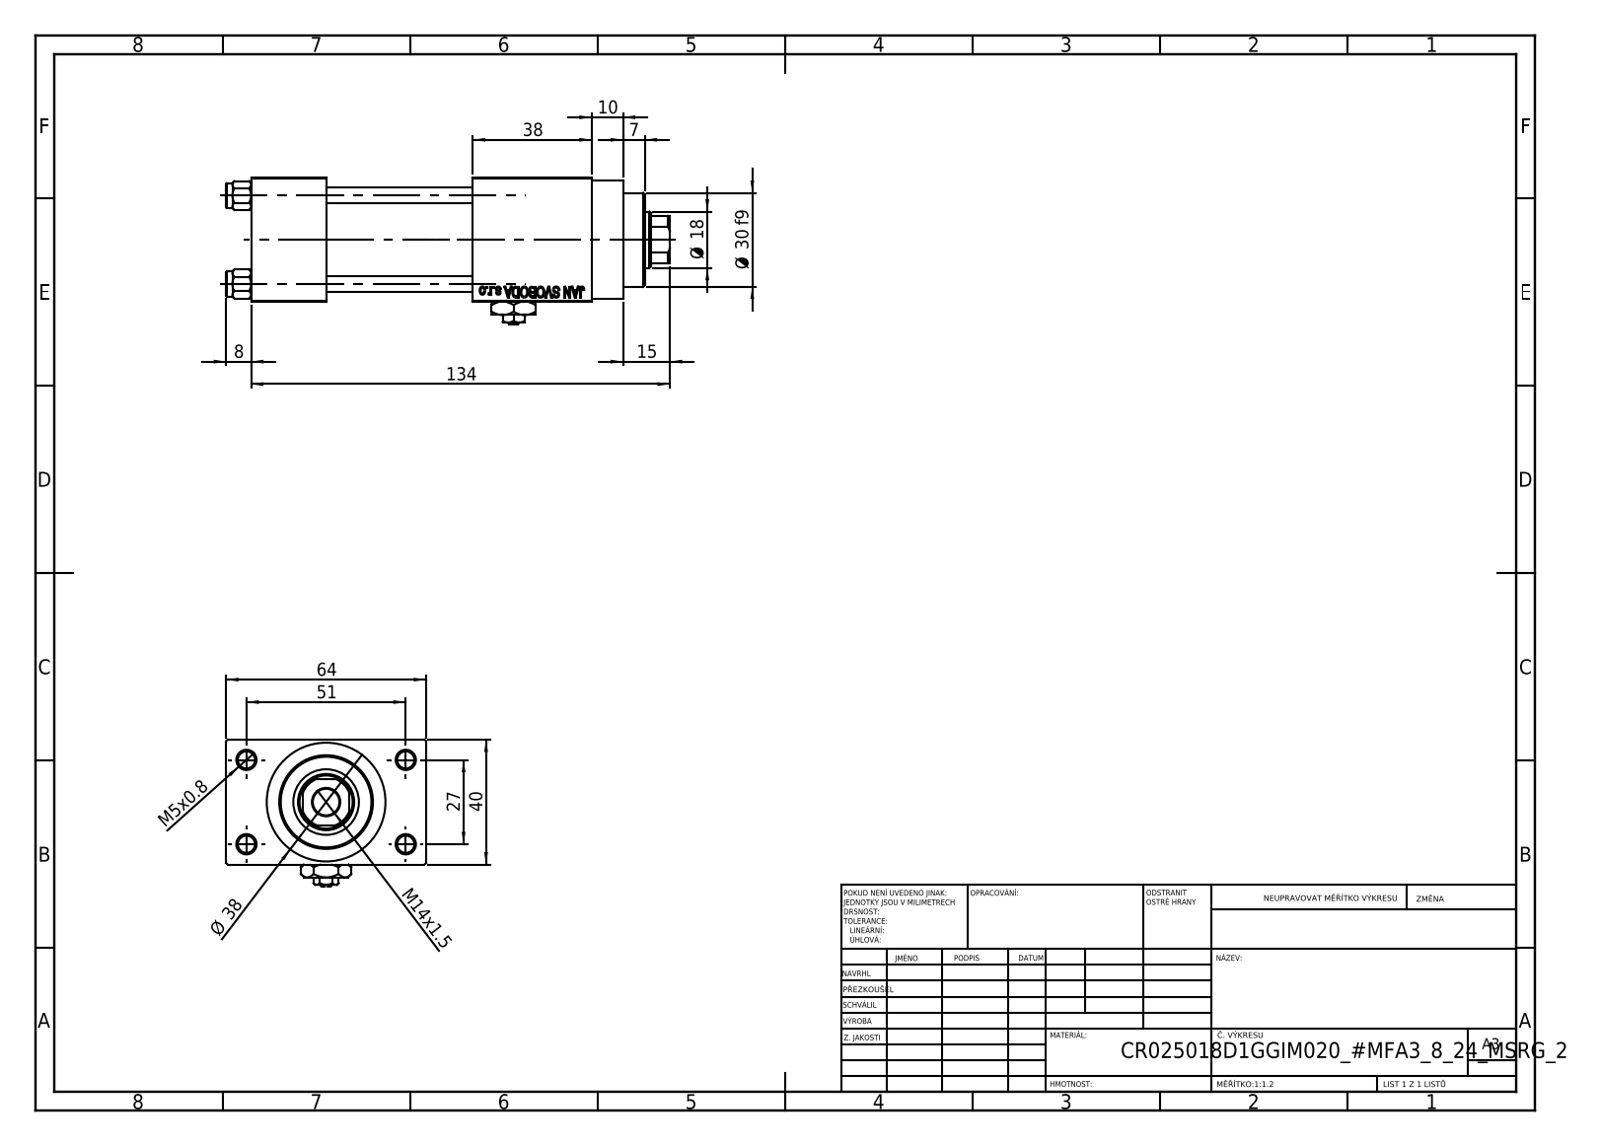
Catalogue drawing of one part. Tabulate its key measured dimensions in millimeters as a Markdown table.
| quantity | value |
| --- | --- |
| part name | NUT_M5_D; V215_VC_A; V215CR_VCP_D; Zatka_pro_OIL_PORT (+2 more) |
| STEP written by | SolidWorks 2019 (CONFIG_CONTROL_DESIGN) |
| units | millimeters |
| bodies | 12 solids, 1147 faces (518 planar, 91 cylindrical, 538 other) |
| overall size | 142 × 64 × 47 |
| volume | 180 837 mm³ |
| surface area | 64 776 mm² |
| round holes (diameter × count) | 5 × 4, 5.5 × 4, 20 × 3, 7 × 2, 13.16 × 2, 8.5 × 1, 18 × 1, 21 × 1, 25 × 1, 30 × 1 |
| round bosses / shafts (diameter × count) | 8 × 4, 38 × 1, 31 × 1 |
| partial cylindrical surfaces (radius × count) | 8.5 × 1 |
| main face-to-face distances | 40, 12, 52, 47, 24, 71, 64, 38, 85, 109 |
| hole center spacings | 11.37, 20.01, 28.3, 28.85, 29.89, 39.66, 48.34, 27 |
